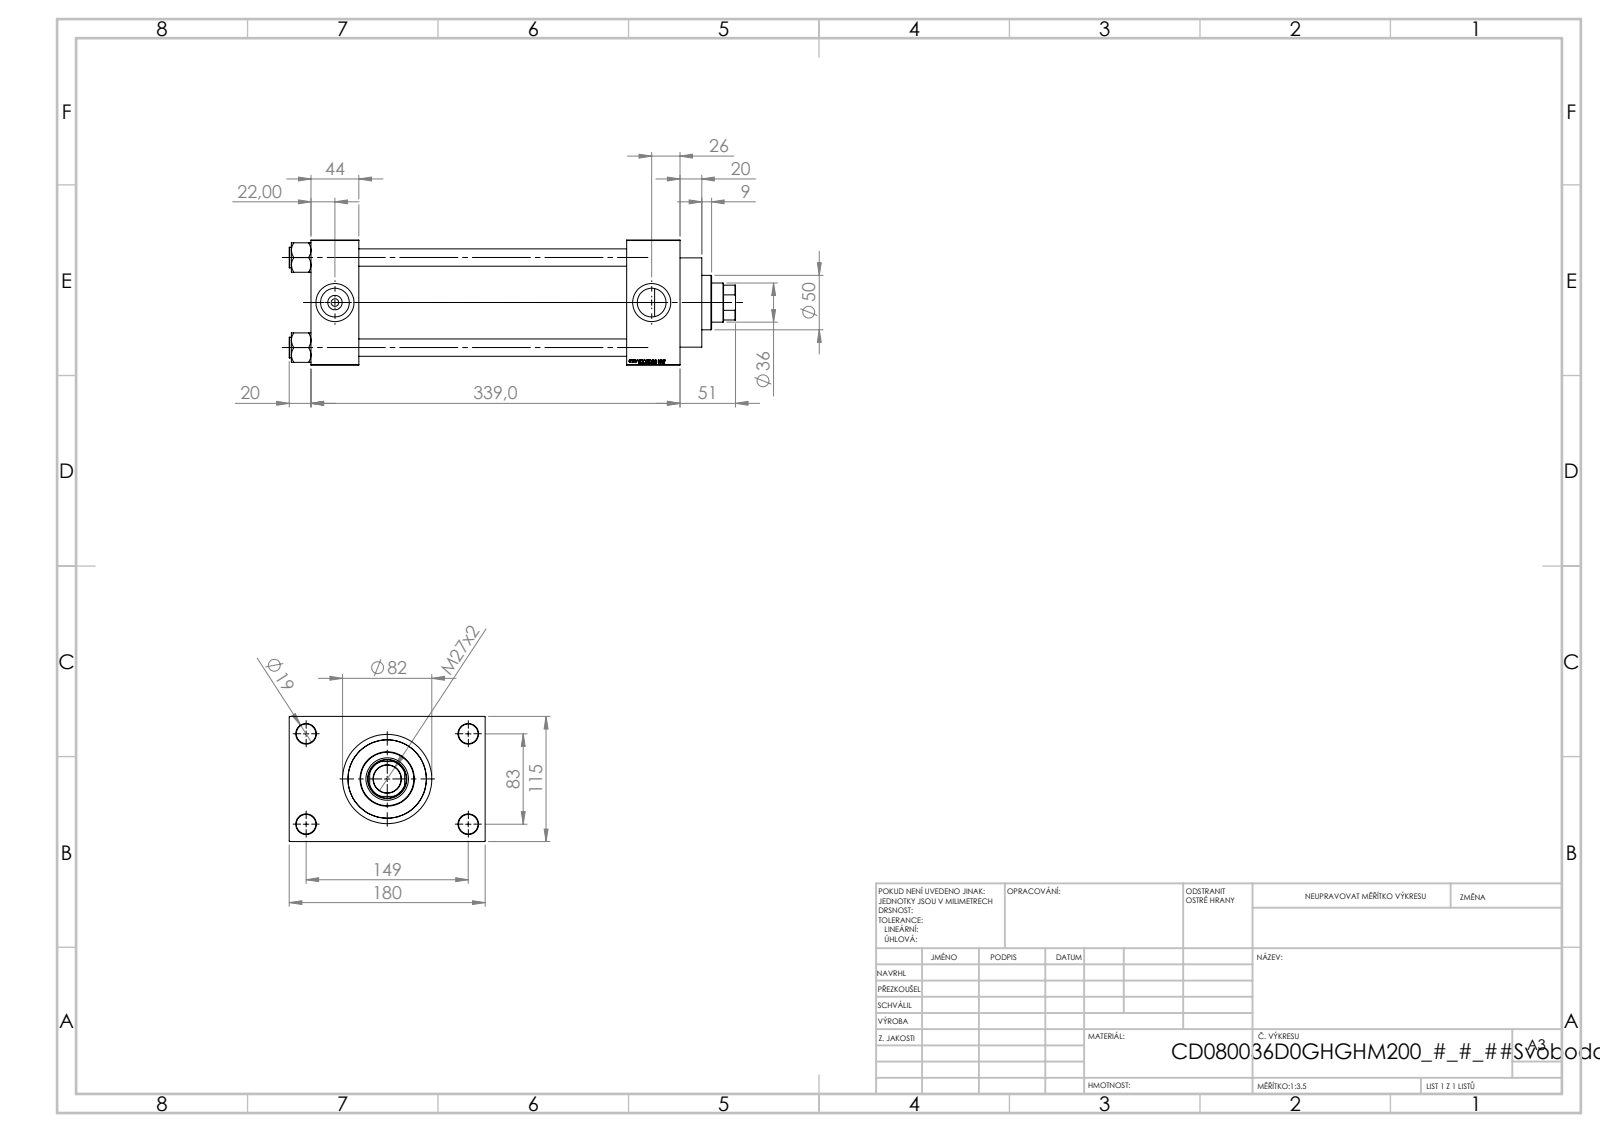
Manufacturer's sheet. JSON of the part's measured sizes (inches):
{"part_name": "V215CD_VCP_D; V215CD_D_TYCINKA; V215CD_D_Body; V215CD_VC_A (+1 more)", "step_written_by": "SolidWorks 2019 (CONFIG_CONTROL_DESIGN)", "units": "inches", "bodies": {"solids": 11, "faces": 1151, "planar": 545, "cylindrical": 88, "other": 518}, "overall_size": [16.142, 7.087, 4.528], "volume_in3": 149.4, "surface_area_in2": 692.9, "round_holes": [[0.63, 4], [0.709, 4], [0.276, 2], [1.041, 2], [1.378, 2], [1.004, 1], [1.417, 1], [1.535, 1], [2.402, 1], [2.835, 1], [3.15, 1]], "round_bosses_or_shafts": [[0.748, 4], [3.386, 1], [3.228, 1], [1.969, 1]], "partial_cylinders_radius": [[0.689, 1]], "face_to_face_distances": [4.528, 9.685, 11.614, 1.929, 1.732, 11.417, 13.346, 1.28, 5.807, 7.087], "hole_center_spacings": [1.305, 2.302, 3.256, 3.357, 3.513, 4.561, 5.607, 3.268]}
